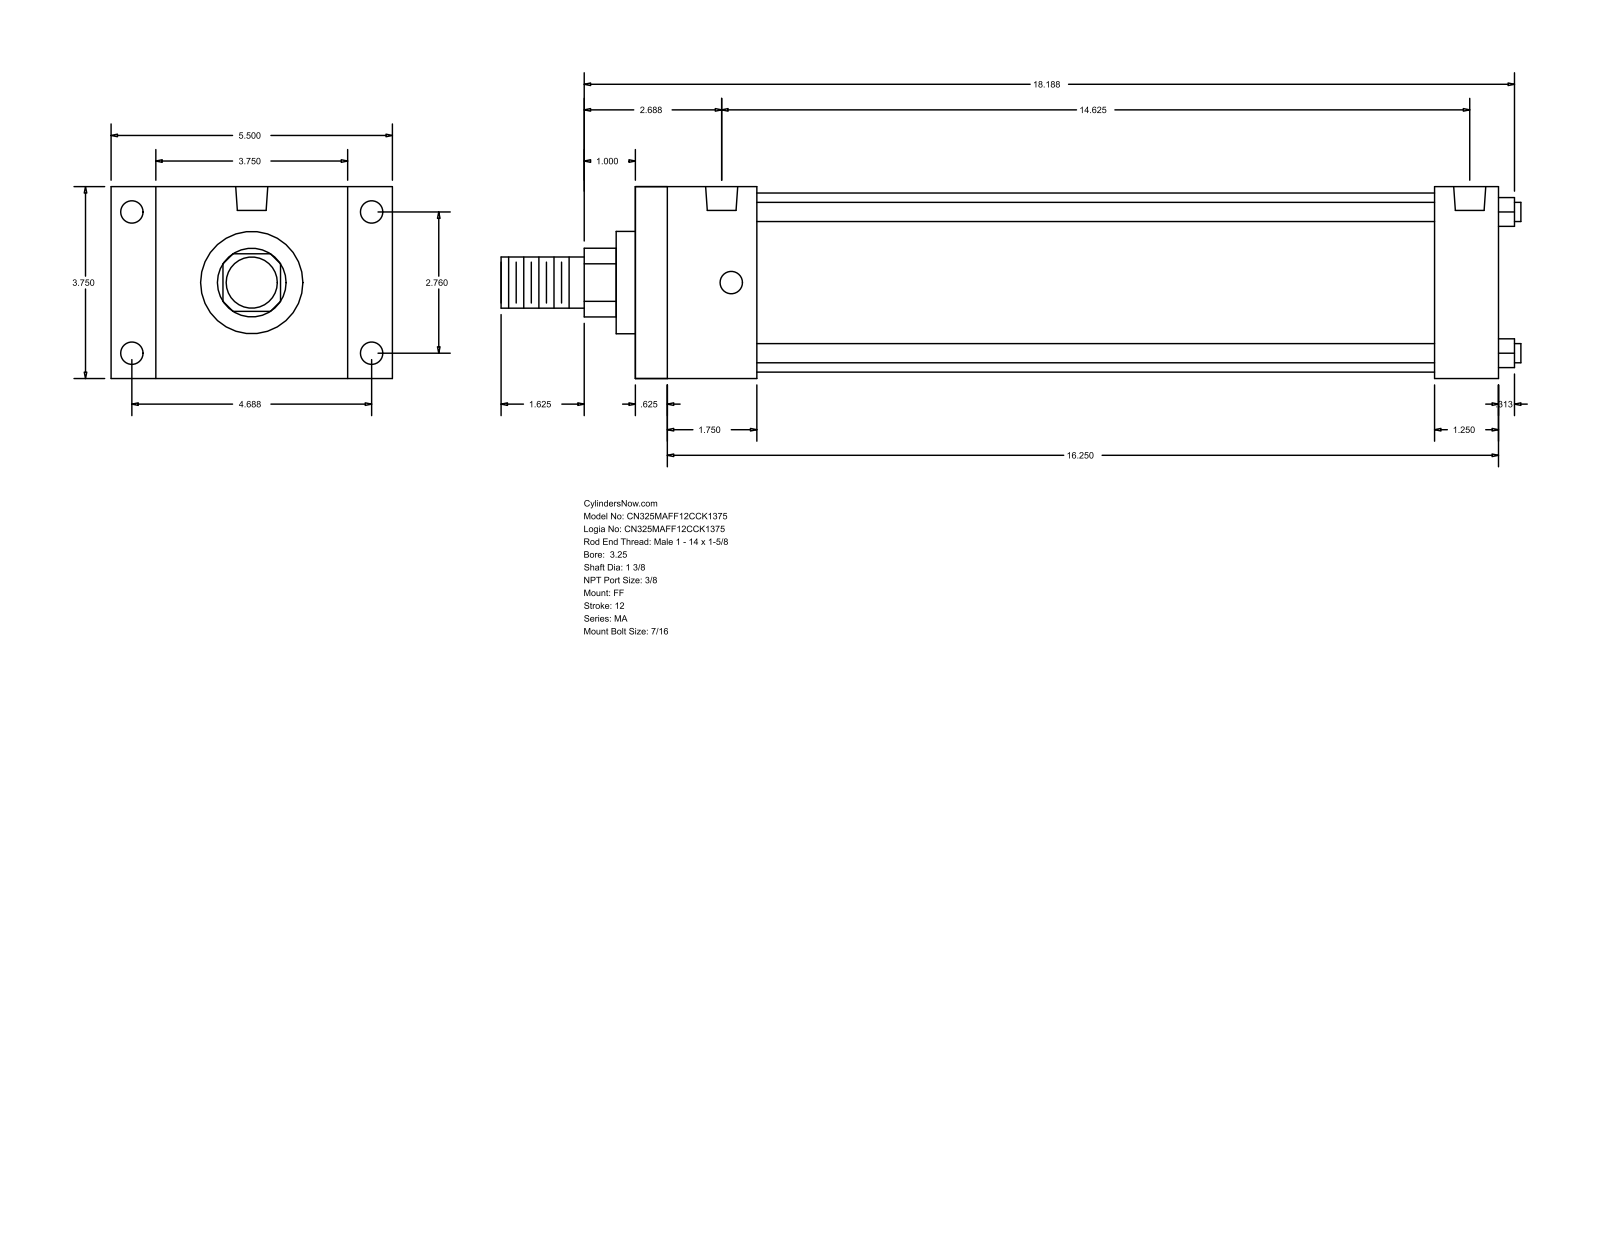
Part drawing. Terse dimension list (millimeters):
name: MA_FF__0325_1.375
written by: GSSL Pune (CONFIG_CONTROL_DESIGN)
unit: mm
bodies: 0 solids, 92 faces (64 planar, 28 cylindrical, 0 other)
size: 506.41 × 139.7 × 95.25
holes: 8× ⌀11.11, 2× ⌀15.93
bosses: 4× ⌀9.53, 1× ⌀88.9, 1× ⌀50.8, 1× ⌀34.92, 1× ⌀25.4
rounds: 1× R17.06
face distances: 95.24, 428.62, 15.87, 412.75, 22.23, 117.47, 60.32, 396.87, 44.45, 381
hole spacings: 70.1, 119.06, 138.16, 361.95, 4.76, 4.77, 366.71, 366.72
